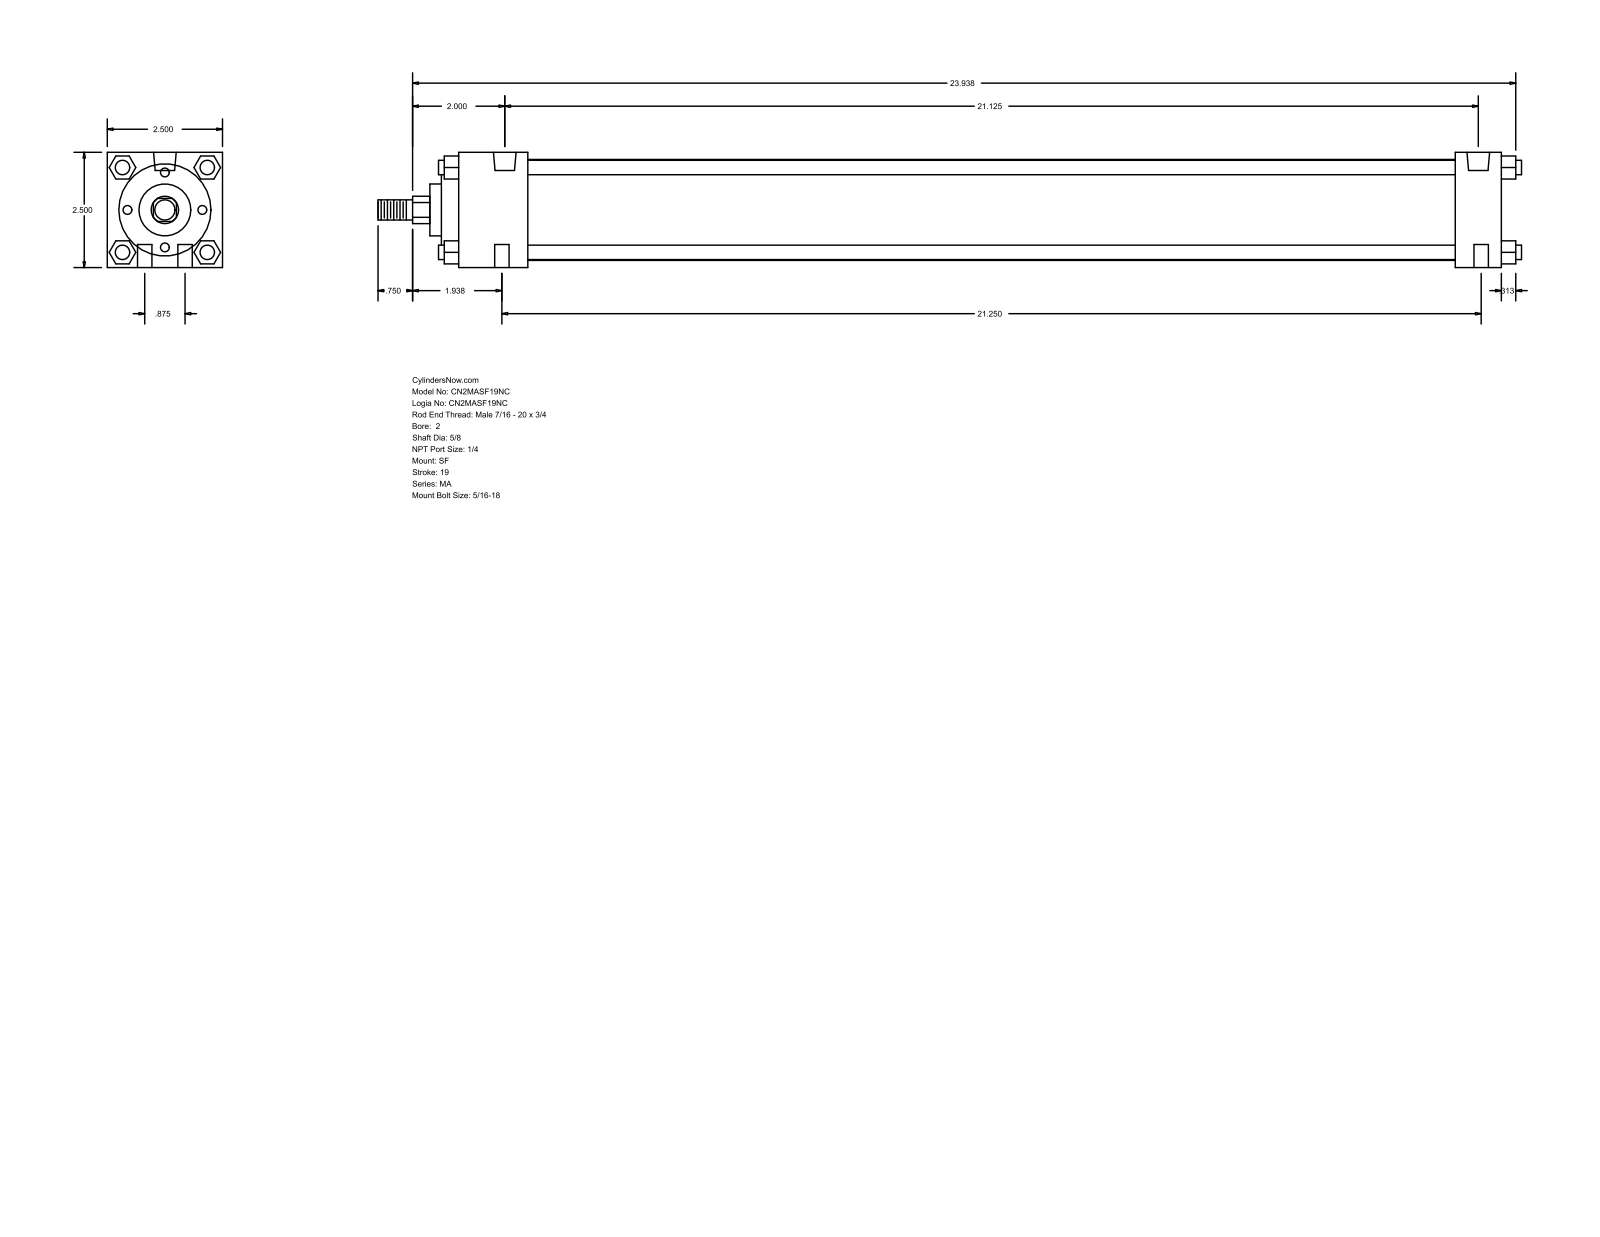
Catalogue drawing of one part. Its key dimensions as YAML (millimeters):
part_name: "MA_SF__0200_0.625"
step_written_by: "GSSL Pune (CONFIG_CONTROL_DESIGN)"
units: millimeters
bodies: {solids: 0, faces: 126, planar: 95, cylindrical: 31, other: 0}
overall_size: [630.24, 63.5, 63.5]
round_holes:
  - {diameter: 7.94, count: 6}
  - {diameter: 12.49, count: 2}
round_bosses_or_shafts:
  - {diameter: 7.94, count: 4}
  - {diameter: 55.63, count: 1}
  - {diameter: 50.8, count: 1}
  - {diameter: 28.57, count: 1}
  - {diameter: 15.88, count: 1}
  - {diameter: 11.11, count: 1}
partial_cylinders:
  - {radius: 7.54, count: 1}
face_to_face_distances: [63.5, 12.7, 38.1, 574.68, 549.27, 25.41, 511.17, 536.58, 9.52, 47.62]
hole_center_spacings: [11.22, 22.22, 536.58, 538.27, 538.28, 539.75, 540.21]
